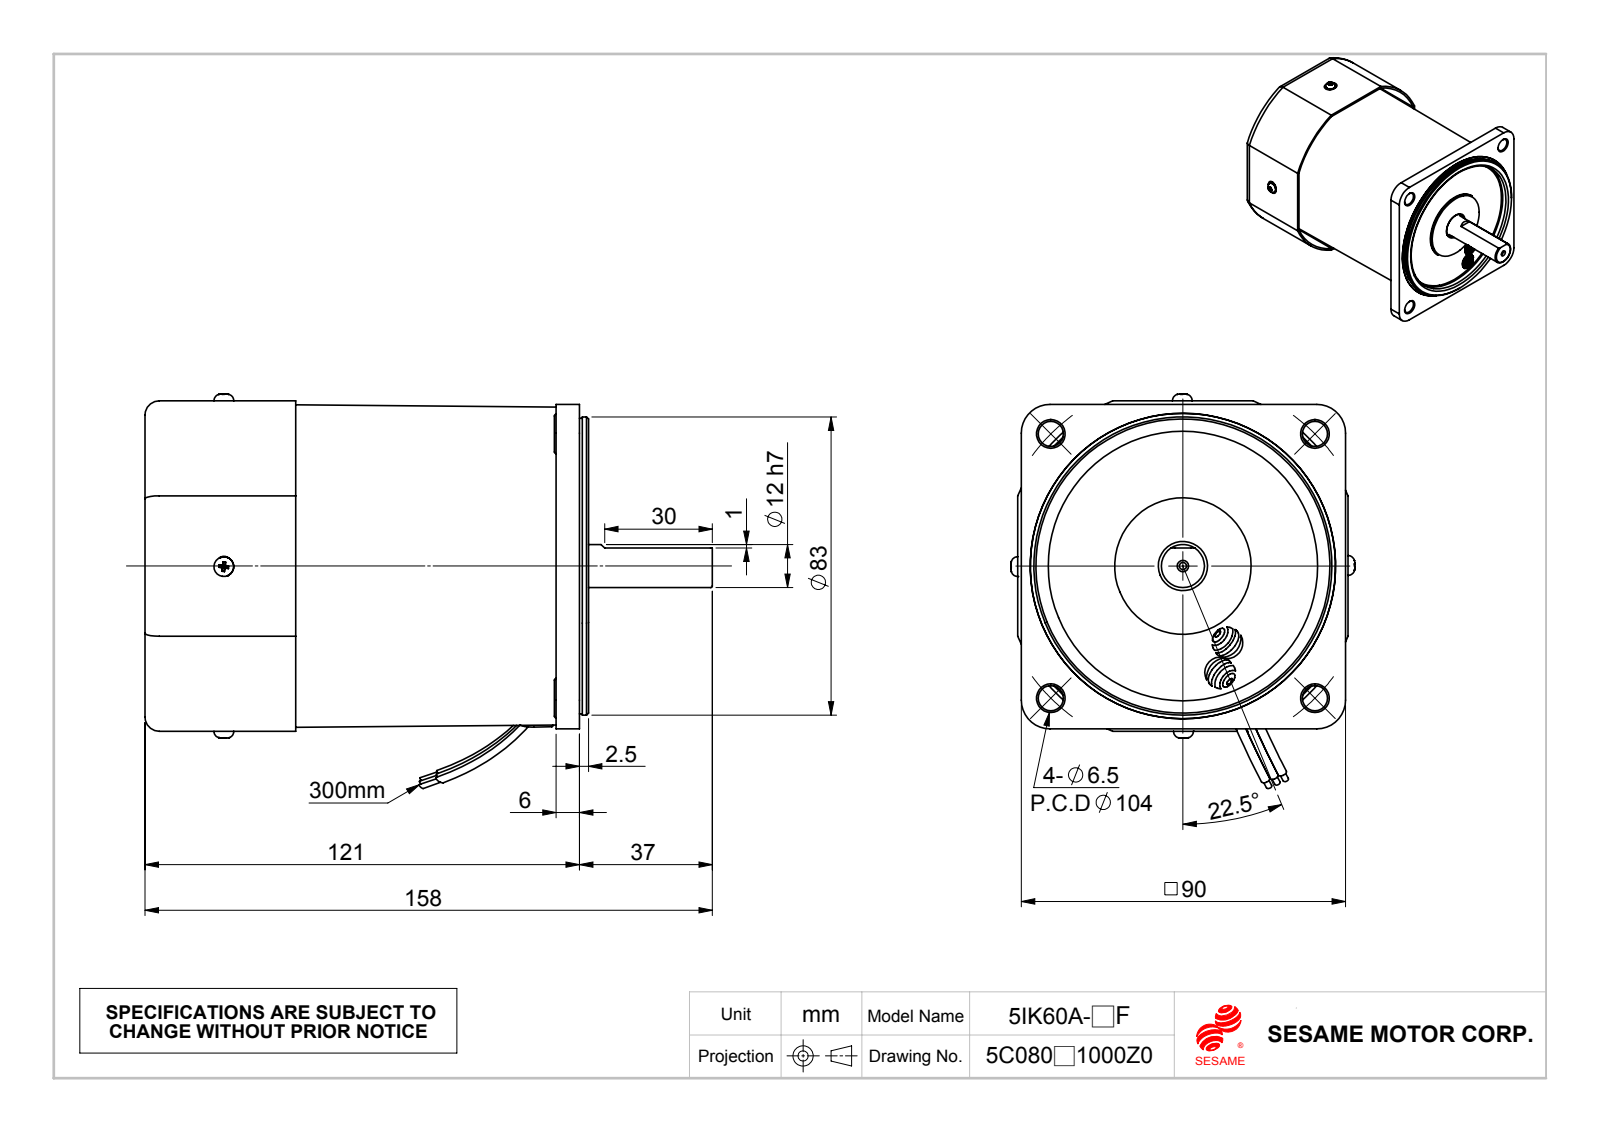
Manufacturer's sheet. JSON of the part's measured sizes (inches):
{"part_name": "60A; 線扣; M560; 風扇蓋FC-9042-21", "step_written_by": "SolidWorks 2010 (CONFIG_CONTROL_DESIGN)", "units": "inches", "bodies": {"solids": 12, "faces": 657, "planar": 199, "cylindrical": 322, "other": 136}, "overall_size": [6.22, 4.324, 3.773], "volume_in3": 41.84, "surface_area_in2": 158.2, "round_holes": [[0.098, 5], [0.276, 4], [0.079, 1], [0.256, 1], [0.283, 1], [0.374, 1], [0.539, 1], [0.945, 1], [1.024, 1], [1.575, 1], [2.126, 1], [2.287, 1]], "round_bosses_or_shafts": [[0.217, 4], [0.118, 4], [3.316, 1], [3.268, 1], [3.236, 1], [1.85, 1], [1.496, 1], [1.22, 1]], "partial_cylinders_radius": [[0.012, 16], [0.01, 8], [0.031, 8], [0.039, 8], [0.059, 8], [0.065, 8], [0.115, 8], [0.008, 4]], "face_to_face_distances": [0.039, 4.665, 3.583, 0.63, 4.035, 4.661, 4.701, 0.035, 4.626, 4.705], "hole_center_spacings": [2.047, 2.895, 4.094]}
